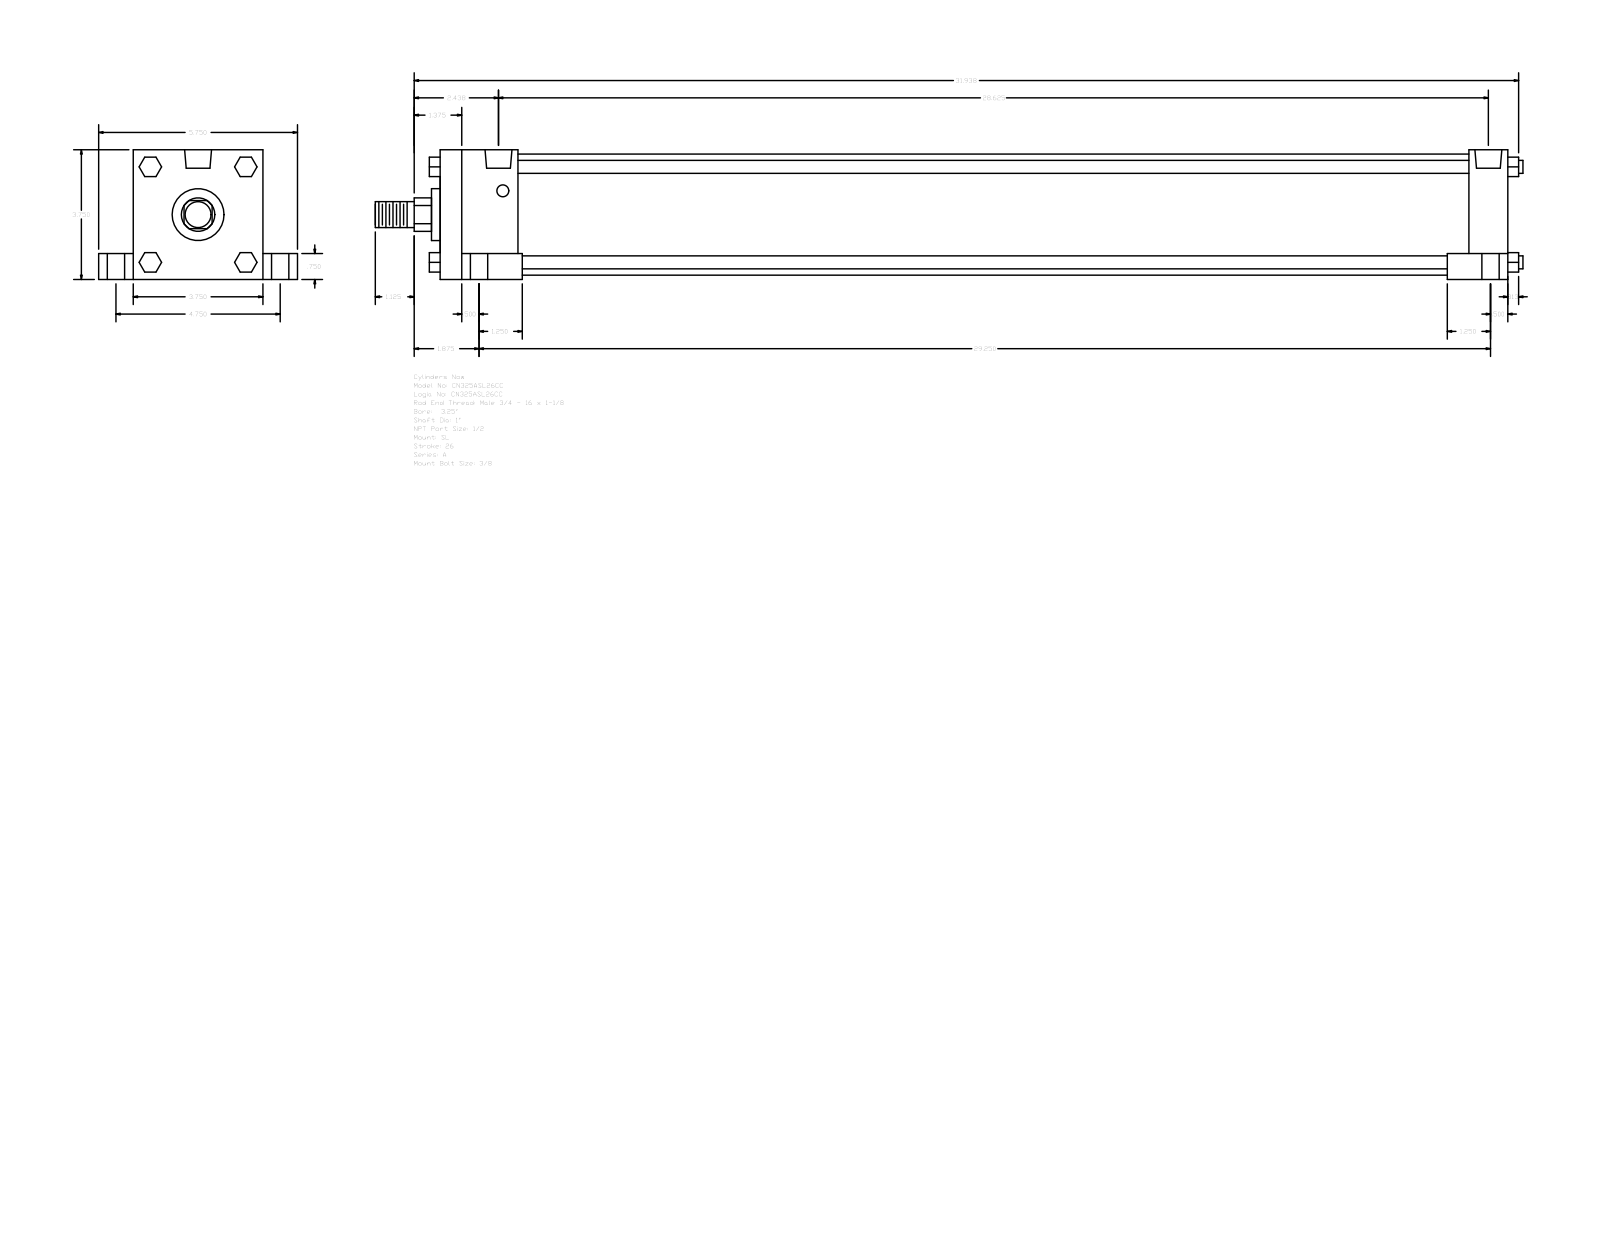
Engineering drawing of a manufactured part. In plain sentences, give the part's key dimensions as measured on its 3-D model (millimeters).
The part is named "A_SL__0325_1". Its 3-D file was written by "GSSL Pune (CONFIG_CONTROL_DESIGN)". It is 0 solids with 150 faces: 114 planar, 36 cylindrical and 0 other. Overall it measures 842.96 by 146.05 by 95.25 millimeters. Round holes: 4 of diameter 8.73, 4 of diameter 12.7, 4 of diameter 19.05, 2 of diameter 19.77. Round bosses or shafts: 4 of diameter 9.53, 1 of diameter 88.9, 1 of diameter 38.1, 1 of diameter 25.4, 1 of diameter 19.05. Partial cylindrical surfaces (rounded edges, fillets, slot ends): 1 of radius 12.29. The main face-to-face distances are 95.24, 784.22, 19.05, 25.41, 120.65, 76.19, 28.57, 57.15, 755.65, 698.5. The hole center spacings are 3.18, 60.35, 60.52, 62, 62.81, 120.66, 720.72, 723.9.
